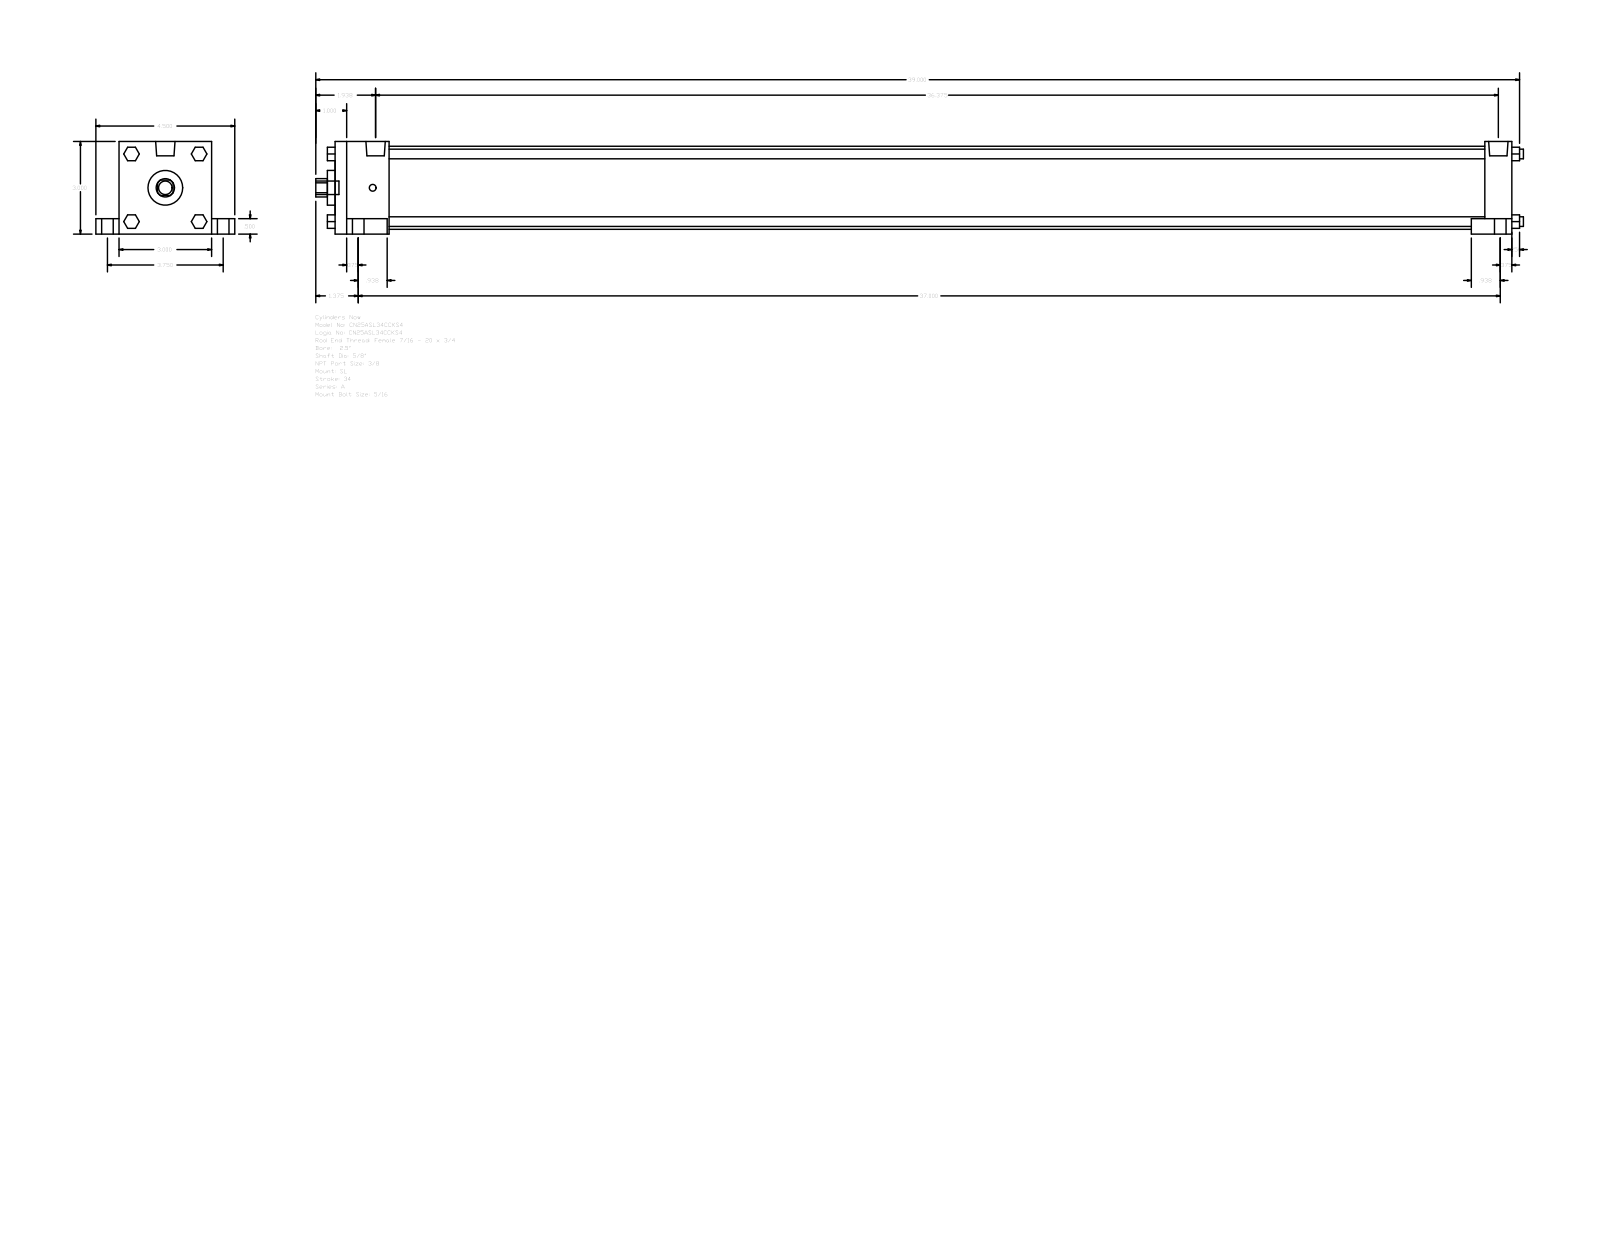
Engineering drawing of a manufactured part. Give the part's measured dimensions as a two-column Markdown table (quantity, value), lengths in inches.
| quantity | value |
| --- | --- |
| part name | A_SL__0250_0.625 |
| STEP written by | GSSL Pune (CONFIG_CONTROL_DESIGN) |
| units | inches |
| bodies | 0 solids, 148 faces (112 planar, 36 cylindrical, 0 other) |
| overall size | 39.125 × 4.5 × 3 |
| round holes (diameter × count) | 0.625 × 1, 1.125 × 1, 2.69 × 1 |
| round bosses / shafts (diameter × count) | 0.625 × 4, 0.375 × 4, 0.313 × 4, 0.219 × 4, 0.627 × 2, 0.437 × 1 |
| partial cylindrical surfaces (radius × count) | 0.297 × 1 |
| main face-to-face distances | 3, 38.125, 1.75, 36.375, 37.25, 35.5, 0.875, 0.5, 2.5, 0.75 |
